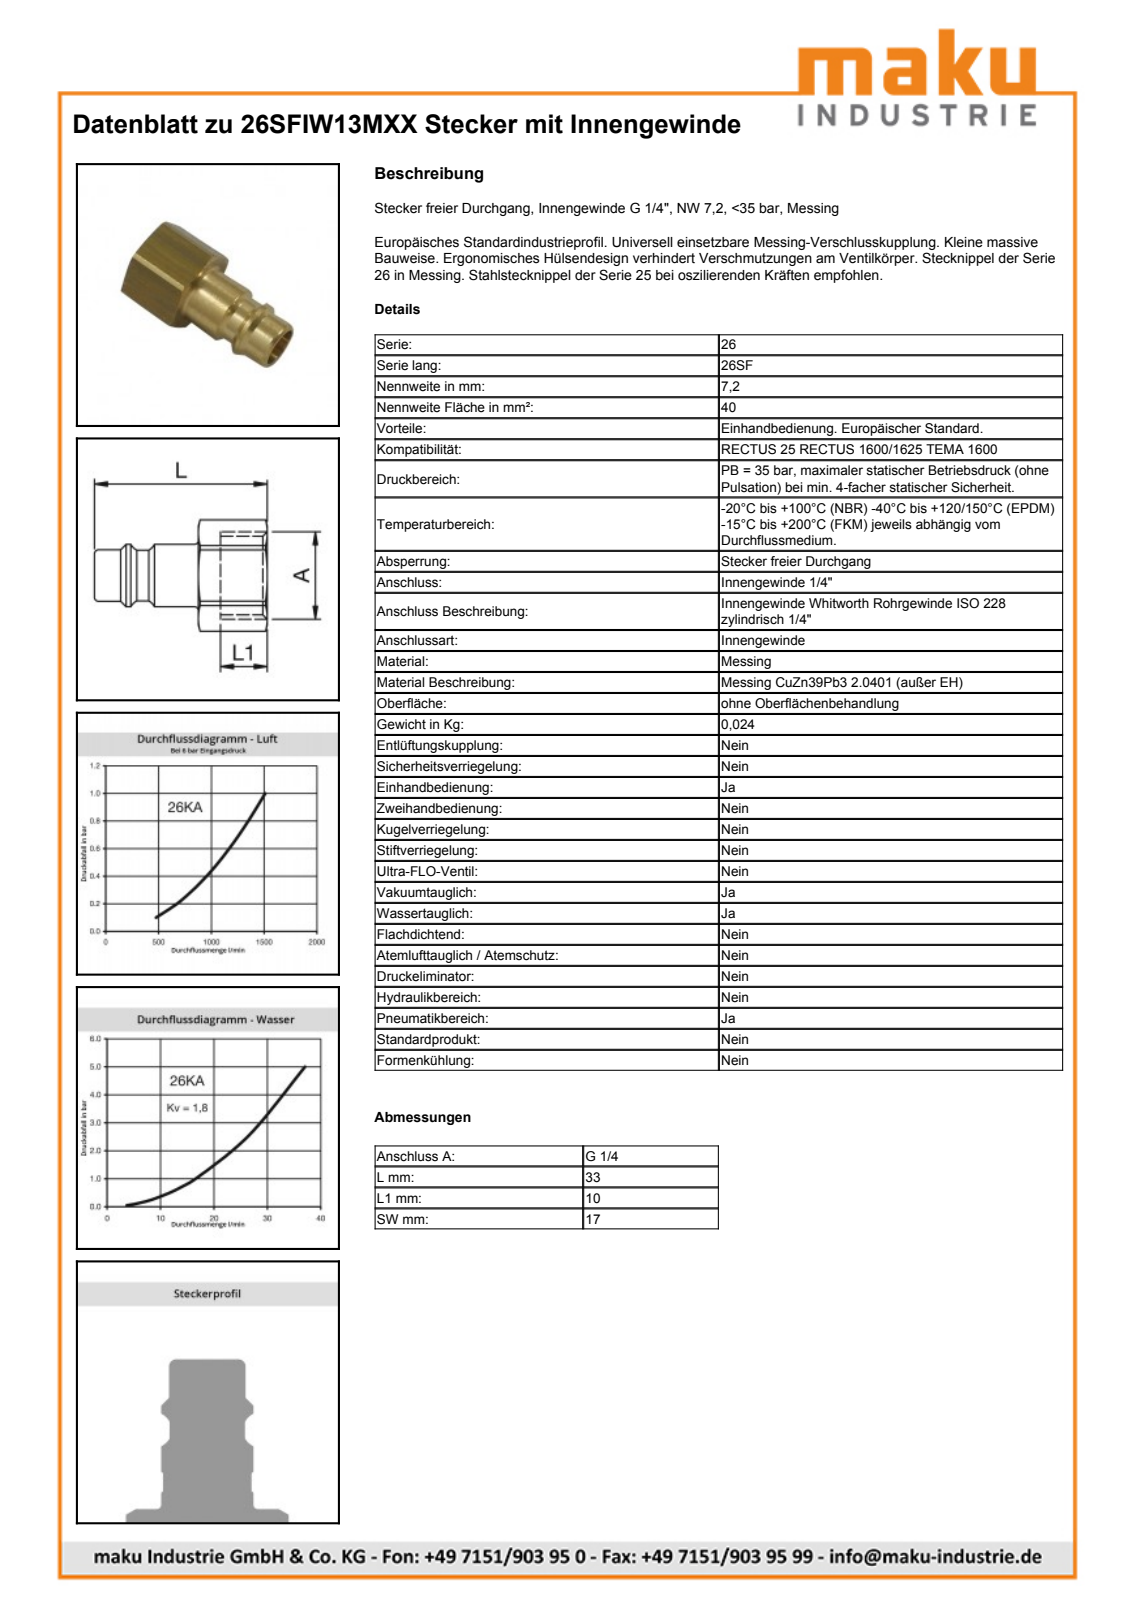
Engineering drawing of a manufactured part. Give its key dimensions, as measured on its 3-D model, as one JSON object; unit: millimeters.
{"part_name": "D103424", "step_written_by": "Autodesk Inventor 2011 (AUTOMOTIVE_DESIGN)", "units": "millimeters", "bodies": {"solids": 1, "faces": 40, "planar": 10, "cylindrical": 12, "other": 18}, "overall_size": [33, 19.15, 17], "volume_mm3": 3010, "surface_area_mm2": 2736, "round_holes": [[7.85, 1], [11.45, 1]], "round_bosses_or_shafts": [[12, 1], [10, 1], [9.75, 1]], "partial_cylinders_radius": [[9.57, 1]], "face_to_face_distances": [17, 13, 3, 10, 20, 23, 33]}
